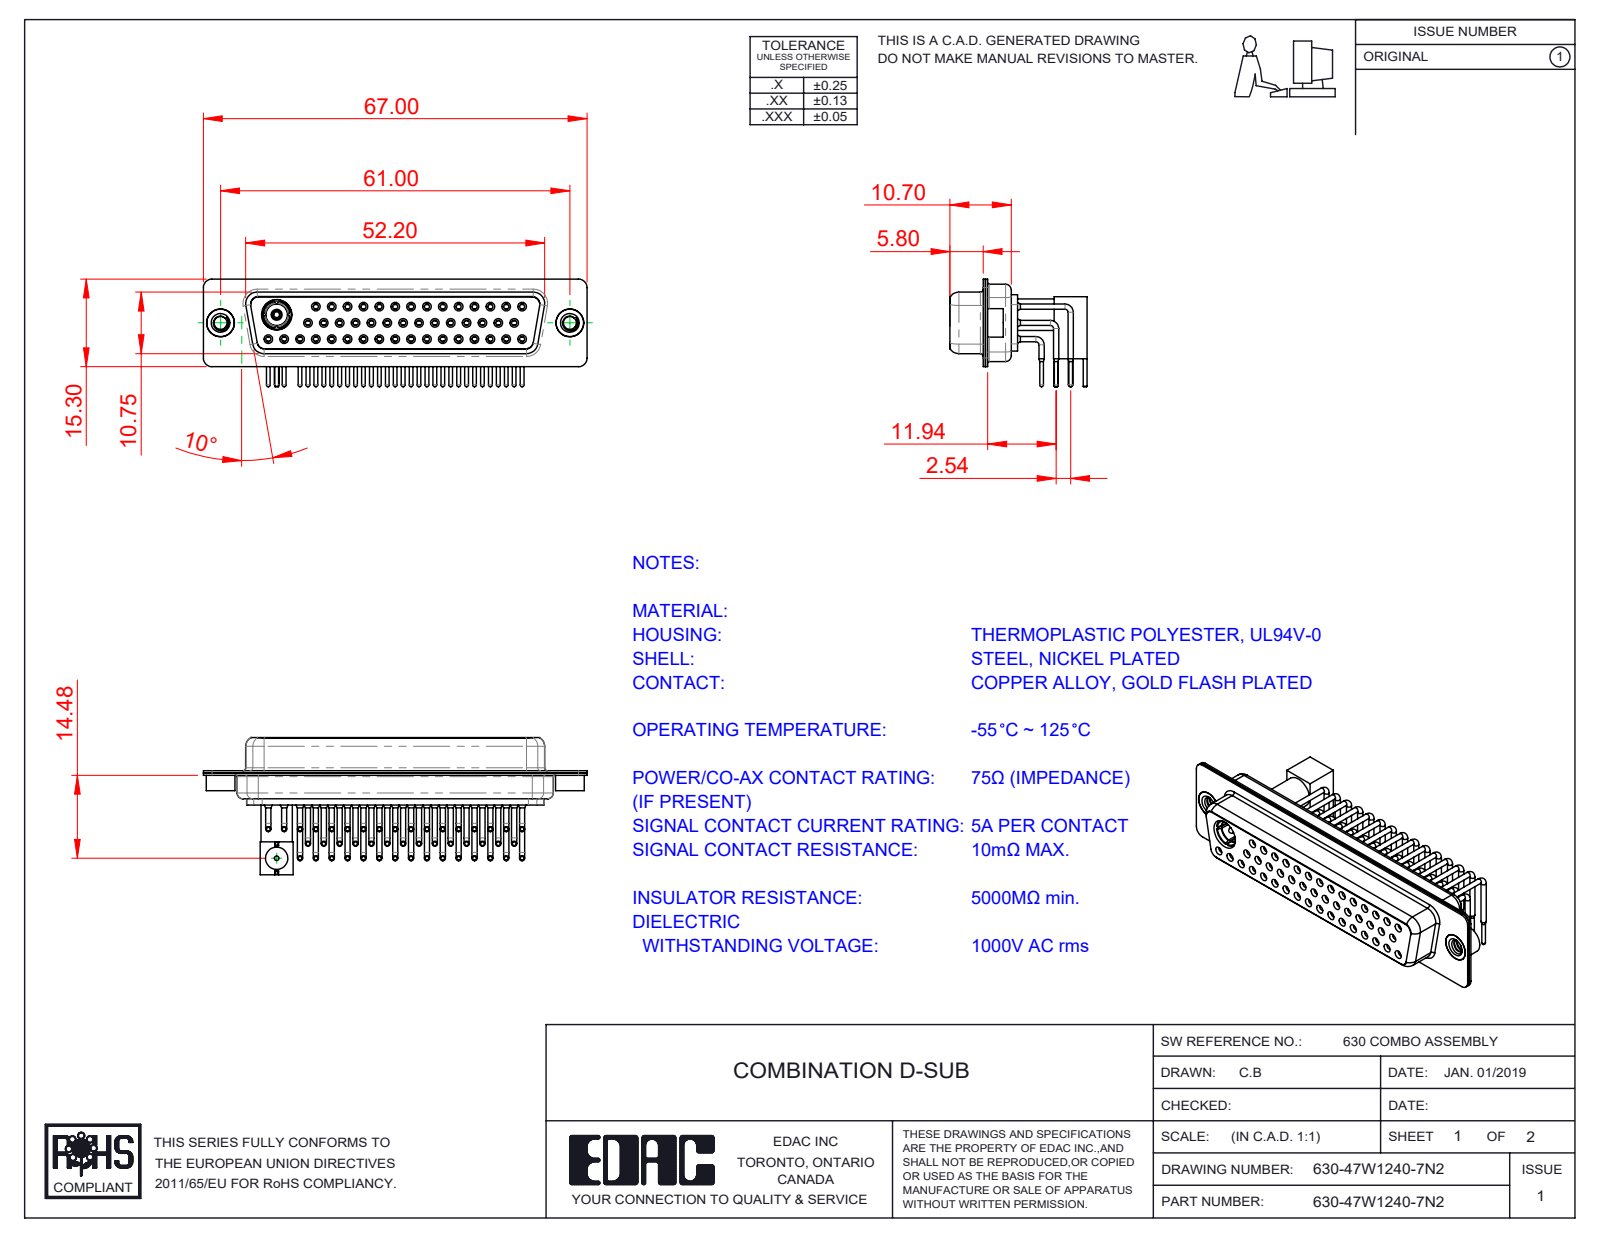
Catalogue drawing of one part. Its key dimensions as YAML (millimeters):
part_name: "Insulator Pin_Straight PC Tail; 630Combo Contact Row 2_50 Contacts; 630Combo Contact Row 3; Co-Ax Plug_RA 50 (+8 more)"
step_written_by: "SolidWorks 2020 (CONFIG_CONTROL_DESIGN)"
units: millimeters
bodies: {solids: 57, faces: 2872, planar: 821, cylindrical: 1252, other: 799}
overall_size: [67, 23.95, 18.8]
volume: 7538
surface_area: 16820
round_holes:
  - {diameter: 1.1, count: 47}
  - {diameter: 1.5, count: 46}
  - {diameter: 0.9, count: 45}
  - {diameter: 2, count: 45}
  - {diameter: 1.6, count: 31}
  - {diameter: 1.7, count: 14}
  - {diameter: 4.85, count: 3}
  - {diameter: 2.26, count: 2}
  - {diameter: 4, count: 2}
  - {diameter: 4.05, count: 2}
  - {diameter: 0.8, count: 1}
  - {diameter: 2.83, count: 1}
round_bosses_or_shafts:
  - {diameter: 0.9, count: 48}
  - {diameter: 0.65, count: 46}
  - {diameter: 1.6, count: 16}
  - {diameter: 5, count: 3}
  - {diameter: 4.95, count: 2}
  - {diameter: 4.8, count: 2}
  - {diameter: 2, count: 2}
  - {diameter: 1.5, count: 2}
partial_cylinders:
  - {radius: 1.5, count: 16}
  - {radius: 1.35, count: 12}
  - {radius: 2, count: 12}
  - {radius: 1.6, count: 8}
  - {radius: 0.25, count: 4}
  - {radius: 0.5, count: 4}
  - {radius: 0.6, count: 4}
  - {radius: 0.65, count: 4}
face_to_face_distances: [0.4, 6, 5.6, 0.8, 11.28, 1.82, 5.8, 11.8, 6.2, 10.35]
hole_center_spacings: [3.16, 2.77, 5.54, 8.31, 11.08, 13.85, 16.62, 19.39]
